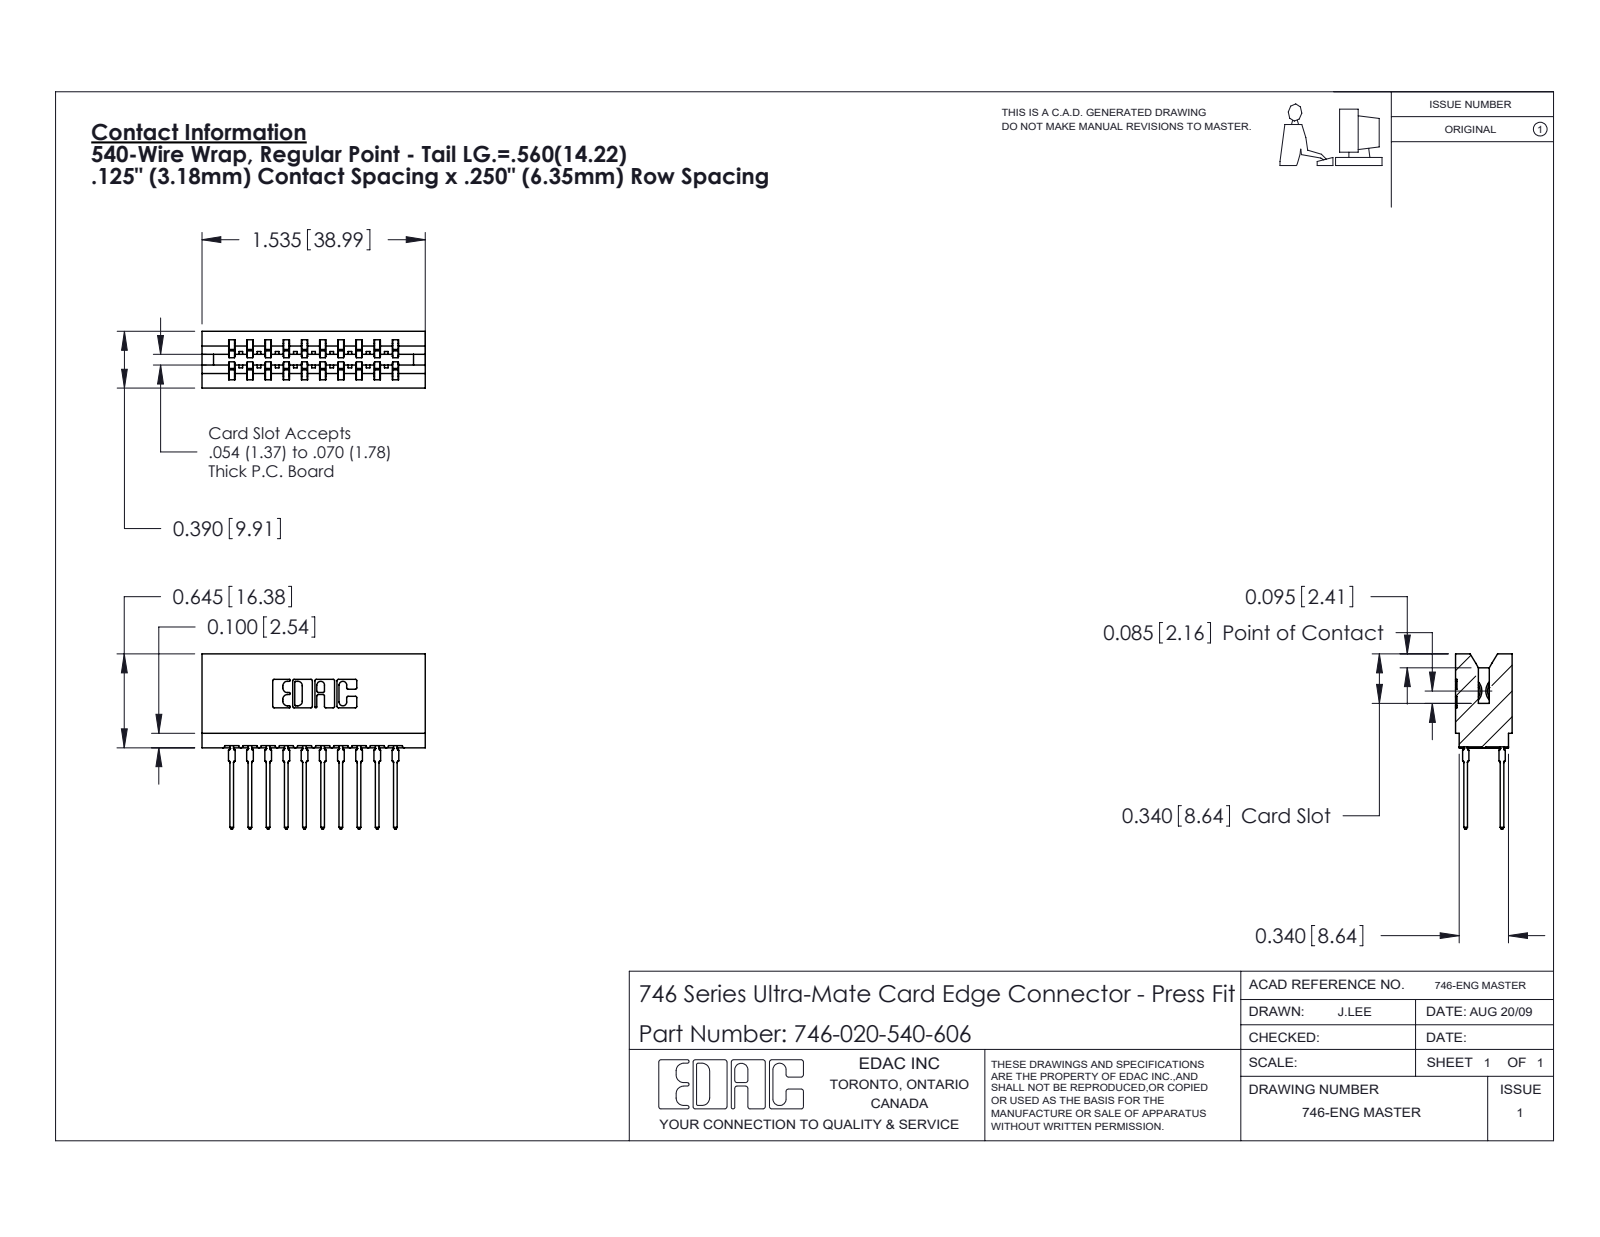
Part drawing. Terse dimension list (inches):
name: 746-292-001_540; 746-020-540-606; 746 Part_.340 Slot Depth - 06
written by: SolidWorks 2020 (CONFIG_CONTROL_DESIGN)
unit: in
bodies: 21 solids, 1888 faces (976 planar, 392 cylindrical, 520 other)
size: 1.535 × 1.204 × 0.39
volume: 0.287 in³; area: 10.25 in²
rounds: 40× R0.021, 22× R0.01, 11× R0.015, 8× R0.005, 8× R0.011, 6× R0.007, 6× R0.031, 3× R0.026
face distances: 0.25, 0.057, 0.333, 0.5, 0.042, 0.125, 0.75, 0.125, 0.083, 0.39
